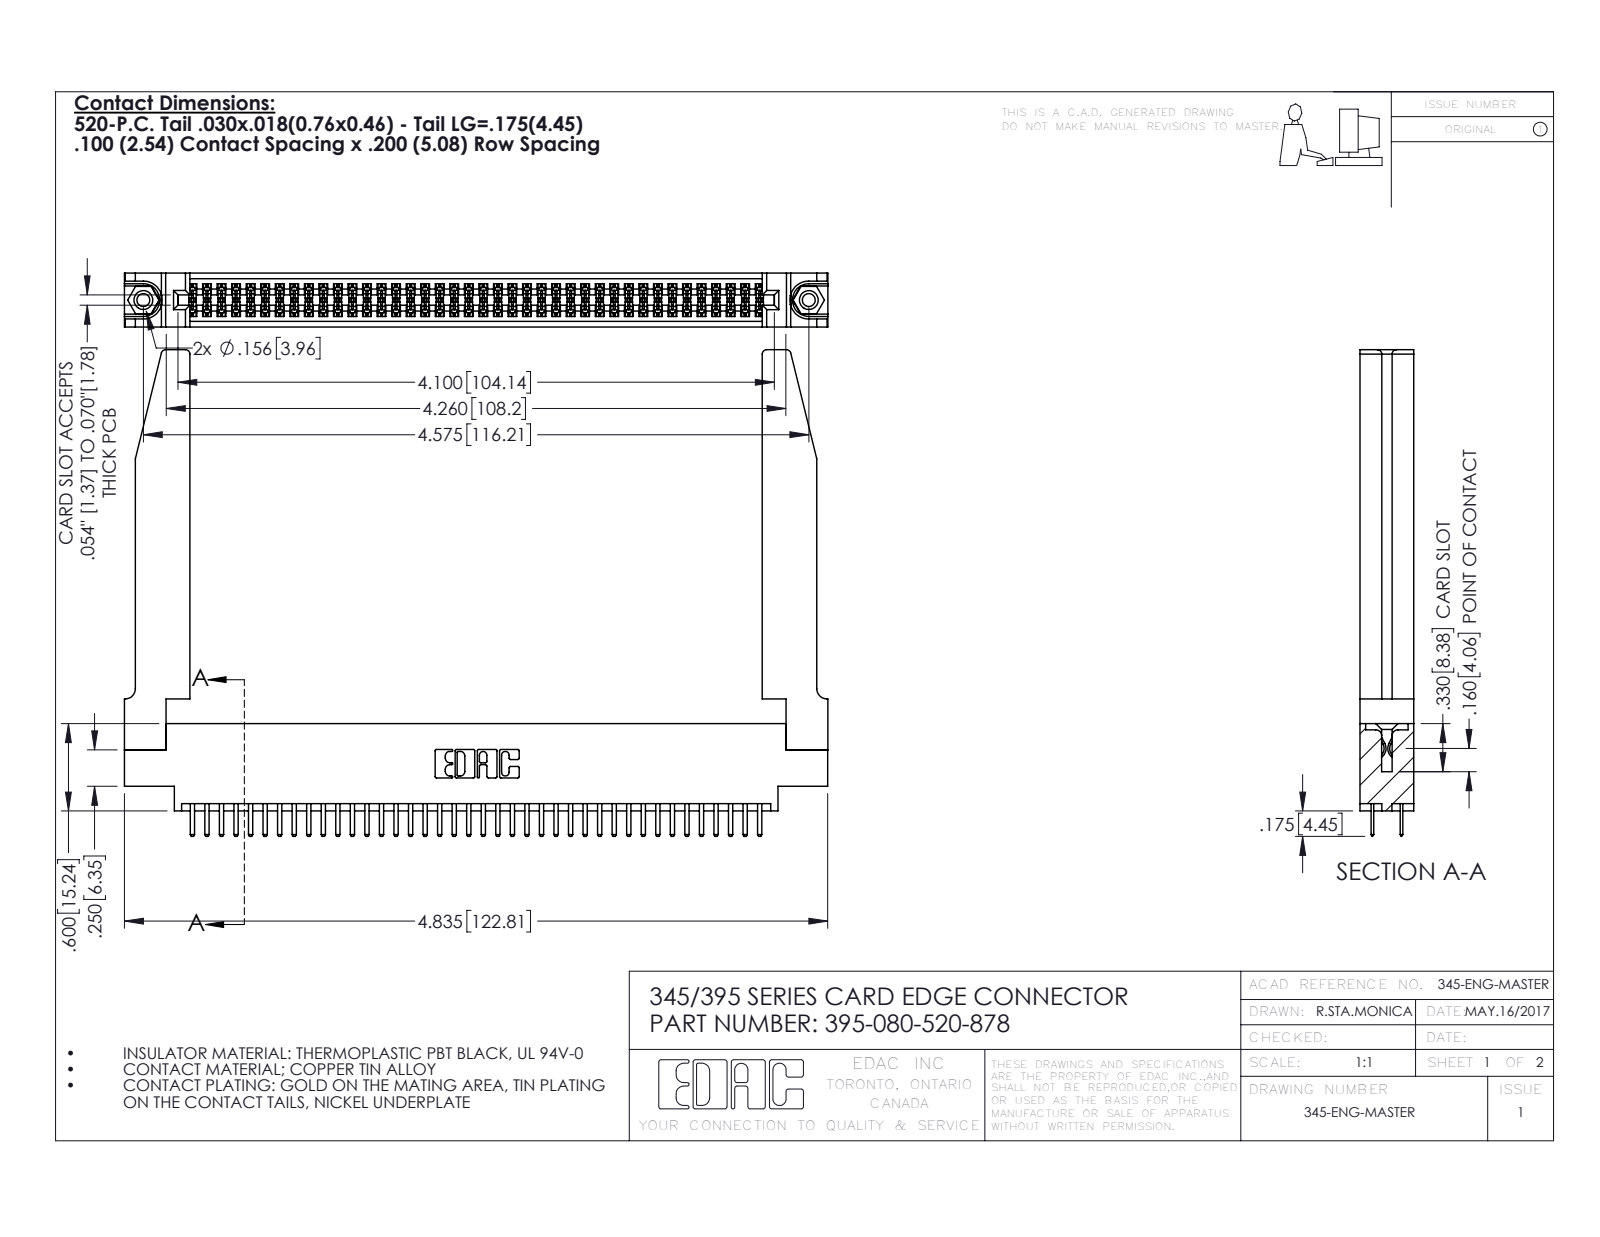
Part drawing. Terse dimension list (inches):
name: 345-250-001_345-250-001-102; 345-292-001_345-293-120; 395-080-520-878; 345-220-078_345-220-078 (+1 more)
written by: SolidWorks 2016 (CONFIG_CONTROL_DESIGN)
unit: in
bodies: 85 solids, 4684 faces (3026 planar, 1606 cylindrical, 52 other)
size: 4.836 × 3.345 × 0.37
volume: 1.192 in³; area: 37.6 in²
holes: 2× ⌀0.089, 2× ⌀0.125, 2× ⌀0.156, 1× ⌀0.064
bosses: 2× ⌀0.155
rounds: 120× R0.006, 84× R0.01, 22× R0.01, 8× R0.03, 6× R0.007, 6× R0.031, 3× R0.026, 2× R0.014
face distances: 0.37, 0.072, 0.298, 0.2, 0.098, 0.272, 0.025, 0.225, 0.022, 0.175
hole spacings: 0.27, 4.339, 4.575
